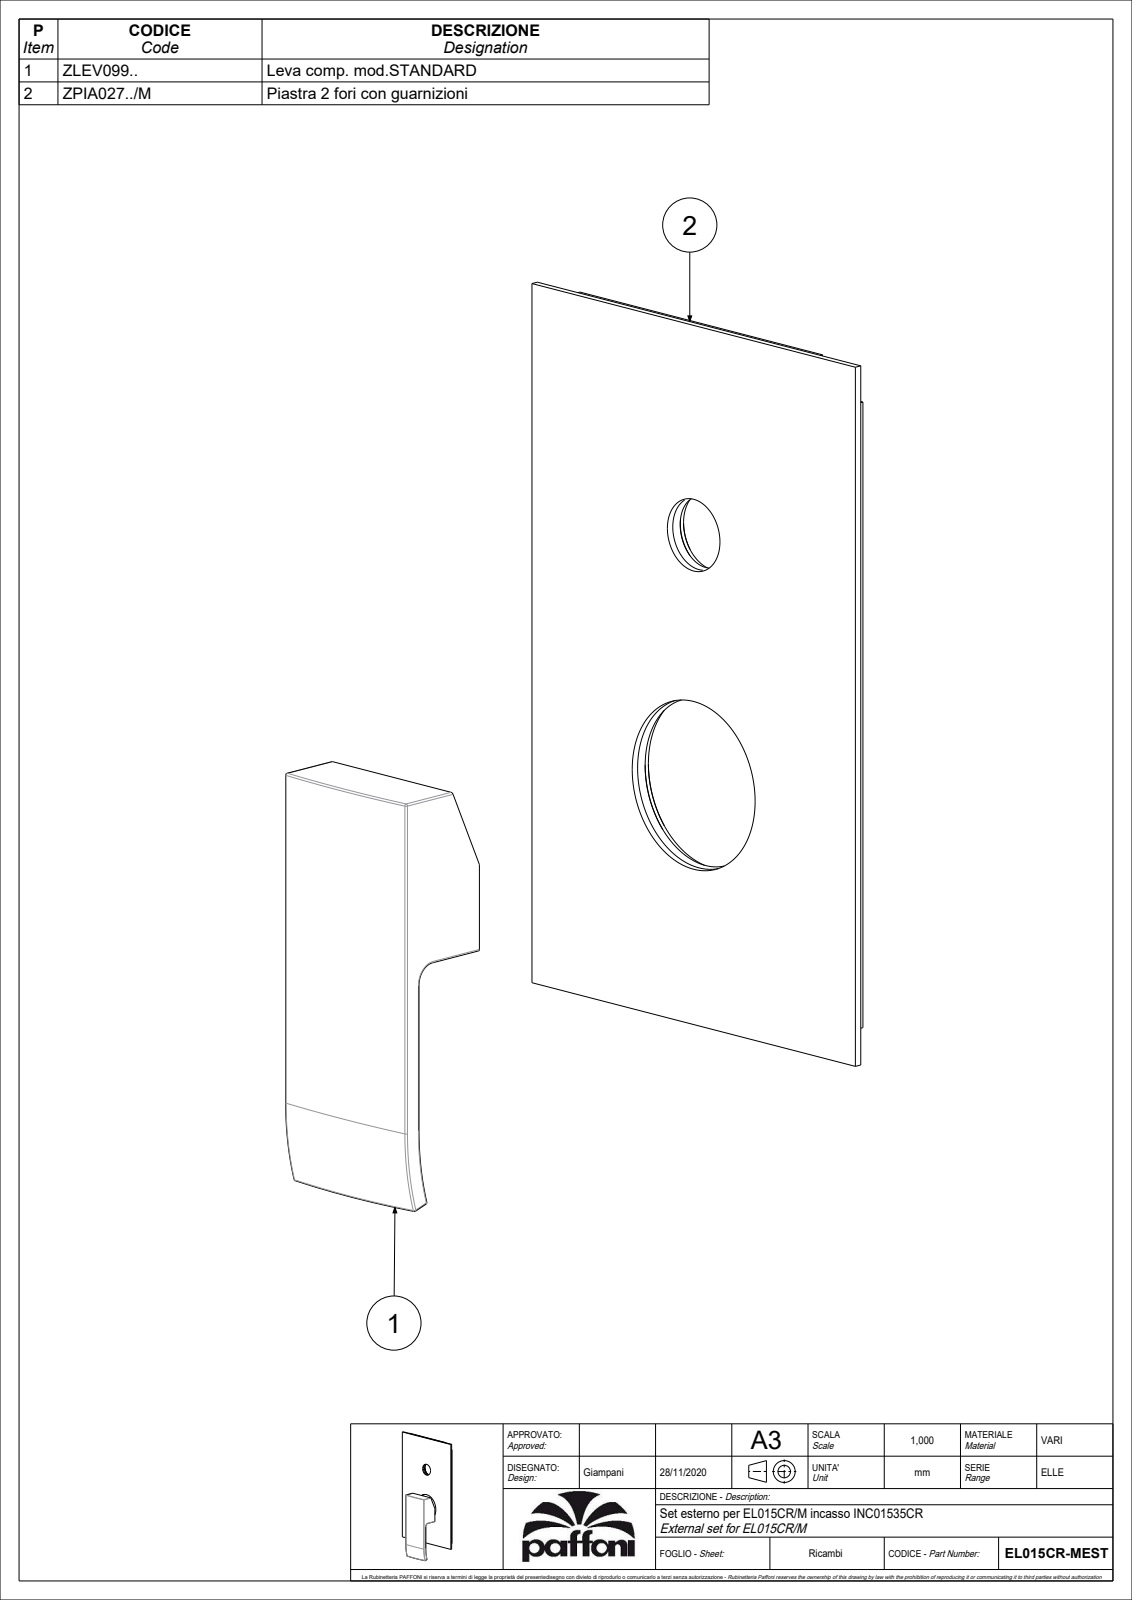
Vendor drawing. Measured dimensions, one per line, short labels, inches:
name: EL015CR-MEST
written by: CREO PARAMETRIC BY PTC INC, 2020044 (CONFIG_CONTROL_DESIGN)
unit: in
bodies: 2 solids, 200 faces (80 planar, 71 cylindrical, 49 other)
size: 8.361 × 4.724 × 1.476
volume: 5.058 in³; area: 106.2 in²
holes: 1× ⌀0.118, 1× ⌀0.13, 1× ⌀0.217, 1× ⌀0.307, 1× ⌀0.768, 1× ⌀0.846, 1× ⌀0.984, 1× ⌀1.795, 1× ⌀1.874, 1× ⌀2.012
bosses: 1× ⌀2.15, 1× ⌀1.122, 1× ⌀0.299, 1× ⌀0.197
rounds: 14× R0.059, 10× R0.02, 4× R0.079, 2× R11.811, 1× R0.089
face distances: 0.079, 0.031, 0.11, 1.772, 1.181, 1.15, 1.071, 1.476, 3.248, 0.217
hole spacings: 2.677
